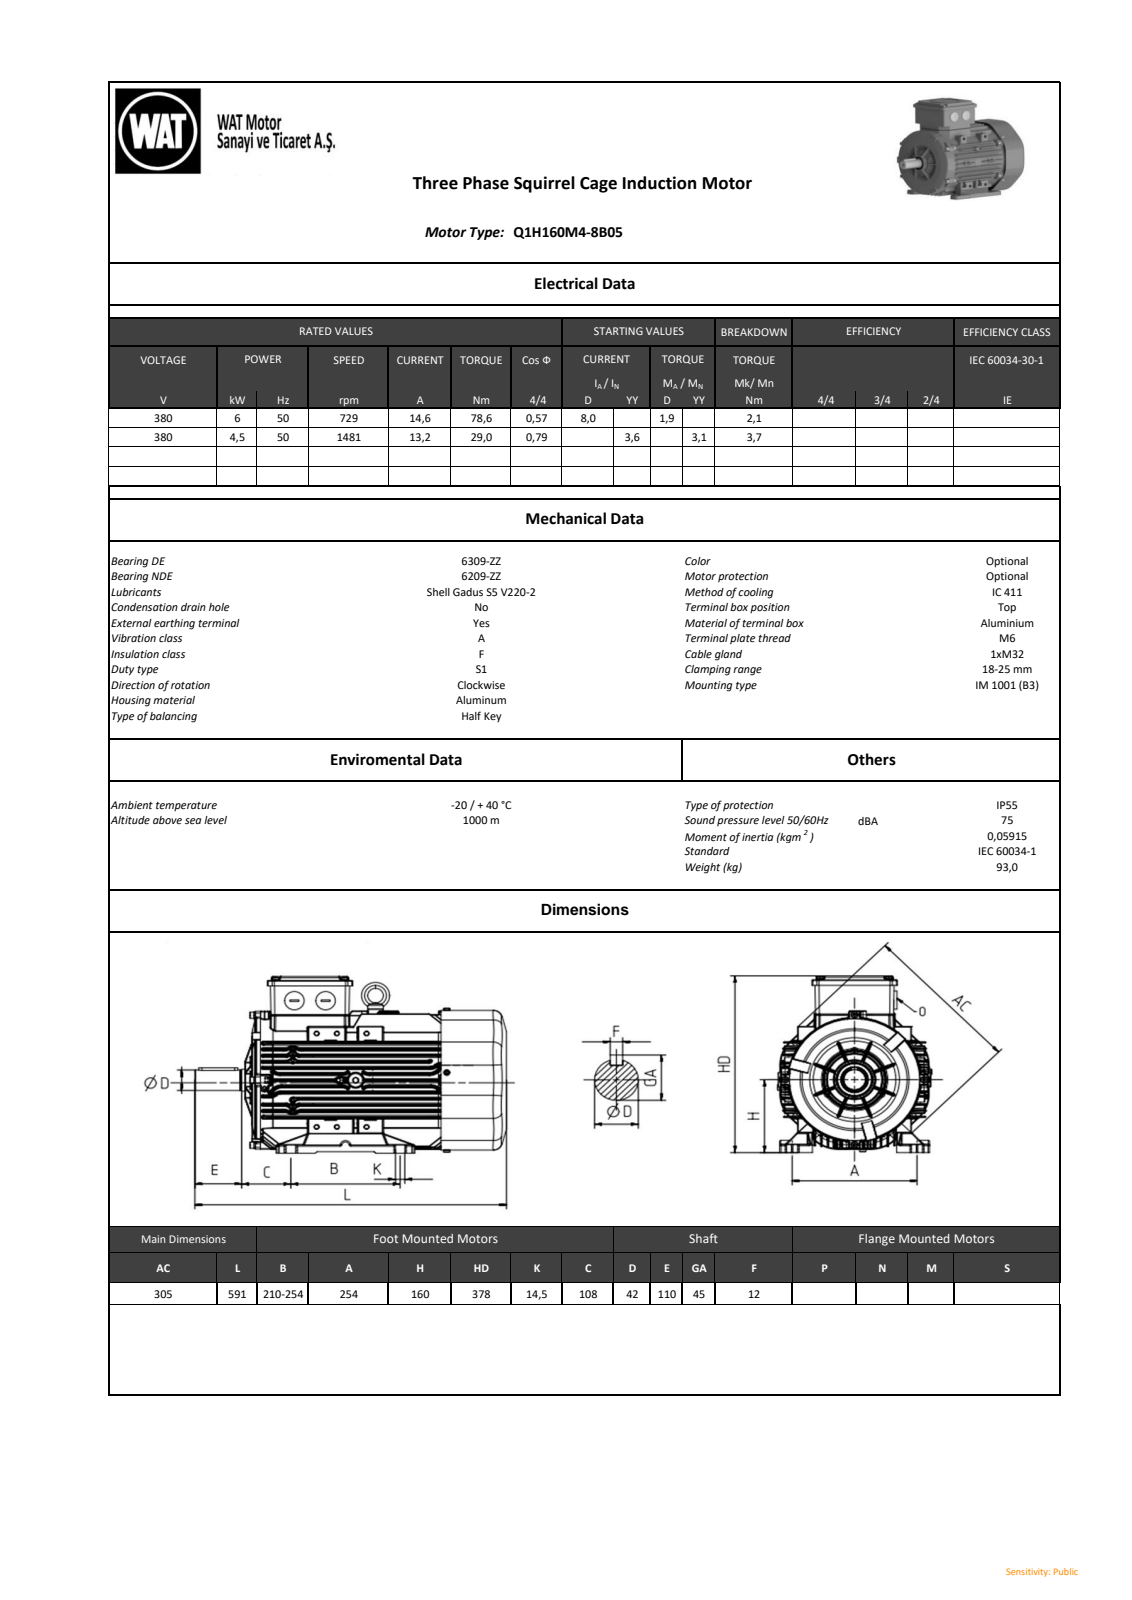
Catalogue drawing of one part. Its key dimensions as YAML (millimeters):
part_name: "QH series_ 160_B3_stp_objects"
step_written_by: "SIEMENS PLM Software NX2206.8101 (AP203_CONFIGURATION_CONTROLLED_3D_DESIGN_OF_MECHANICAL_PARTS_AND_ASSEMBLIES_MIM_LF)"
units: millimeters
bodies: {solids: 0, faces: 7928, planar: 2030, cylindrical: 3438, other: 2460}
overall_size: [591, 377.75, 314]
round_holes:
  - {diameter: 10, count: 1}
  - {diameter: 14, count: 1}
  - {diameter: 17, count: 1}
  - {diameter: 72, count: 1}
  - {diameter: 85.63, count: 1}
  - {diameter: 114, count: 1}
  - {diameter: 134, count: 1}
  - {diameter: 154, count: 1}
  - {diameter: 174, count: 1}
  - {diameter: 194, count: 1}
round_bosses_or_shafts:
  - {diameter: 16, count: 4}
  - {diameter: 13.4, count: 4}
  - {diameter: 13, count: 4}
  - {diameter: 10, count: 4}
  - {diameter: 8, count: 4}
  - {diameter: 38, count: 2}
  - {diameter: 272.5, count: 1}
  - {diameter: 178, count: 1}
partial_cylinders:
  - {radius: 1, count: 816}
  - {radius: 0.5, count: 719}
  - {radius: 4, count: 129}
  - {radius: 2.5, count: 65}
  - {radius: 5, count: 51}
  - {radius: 3, count: 33}
  - {radius: 5.5, count: 16}
  - {radius: 95.6, count: 15}
face_to_face_distances: [168, 144, 11.92, 9.62, 120, 14.77, 168.39, 158.77, 24.39, 11.85]
